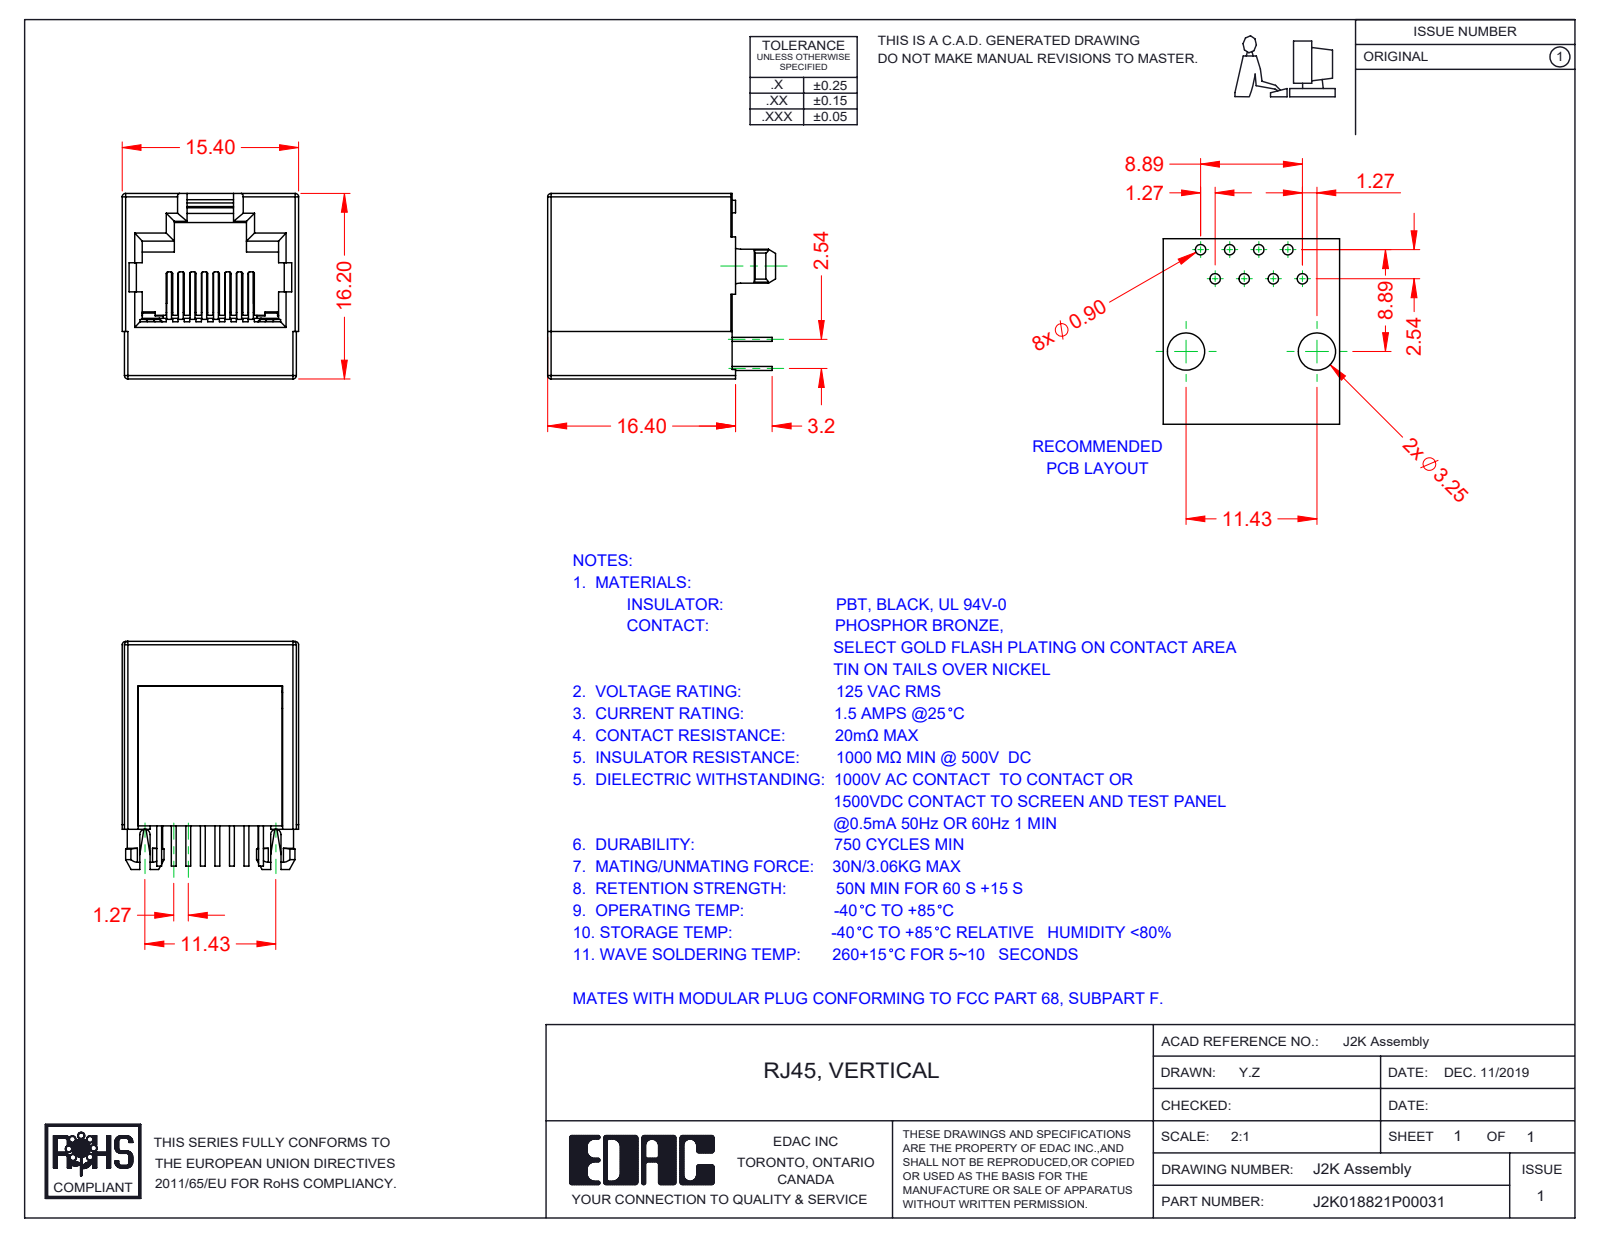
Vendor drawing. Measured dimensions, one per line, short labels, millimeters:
name: 2K Contact Lock; RJ2K018821P00031; 2K Insulator; 2K Contacts
written by: SolidWorks 2016 (CONFIG_CONTROL_DESIGN)
unit: mm
bodies: 10 solids, 723 faces (586 planar, 113 cylindrical, 24 other)
size: 19.9 × 16.2 × 15.4
volume: 2 473 mm³; area: 3 962 mm²
bosses: 2× ⌀3.1, 2× ⌀1.1
rounds: 16× R0.15, 10× R0.3, 3× R0.5, 2× R0.1, 2× R0.2, 2× R0.45, 2× R0.6, 2× R0.95
face distances: 16.2, 15.4, 1.4, 14, 1.2, 13.8, 15.2, 0.35, 0.5, 15
